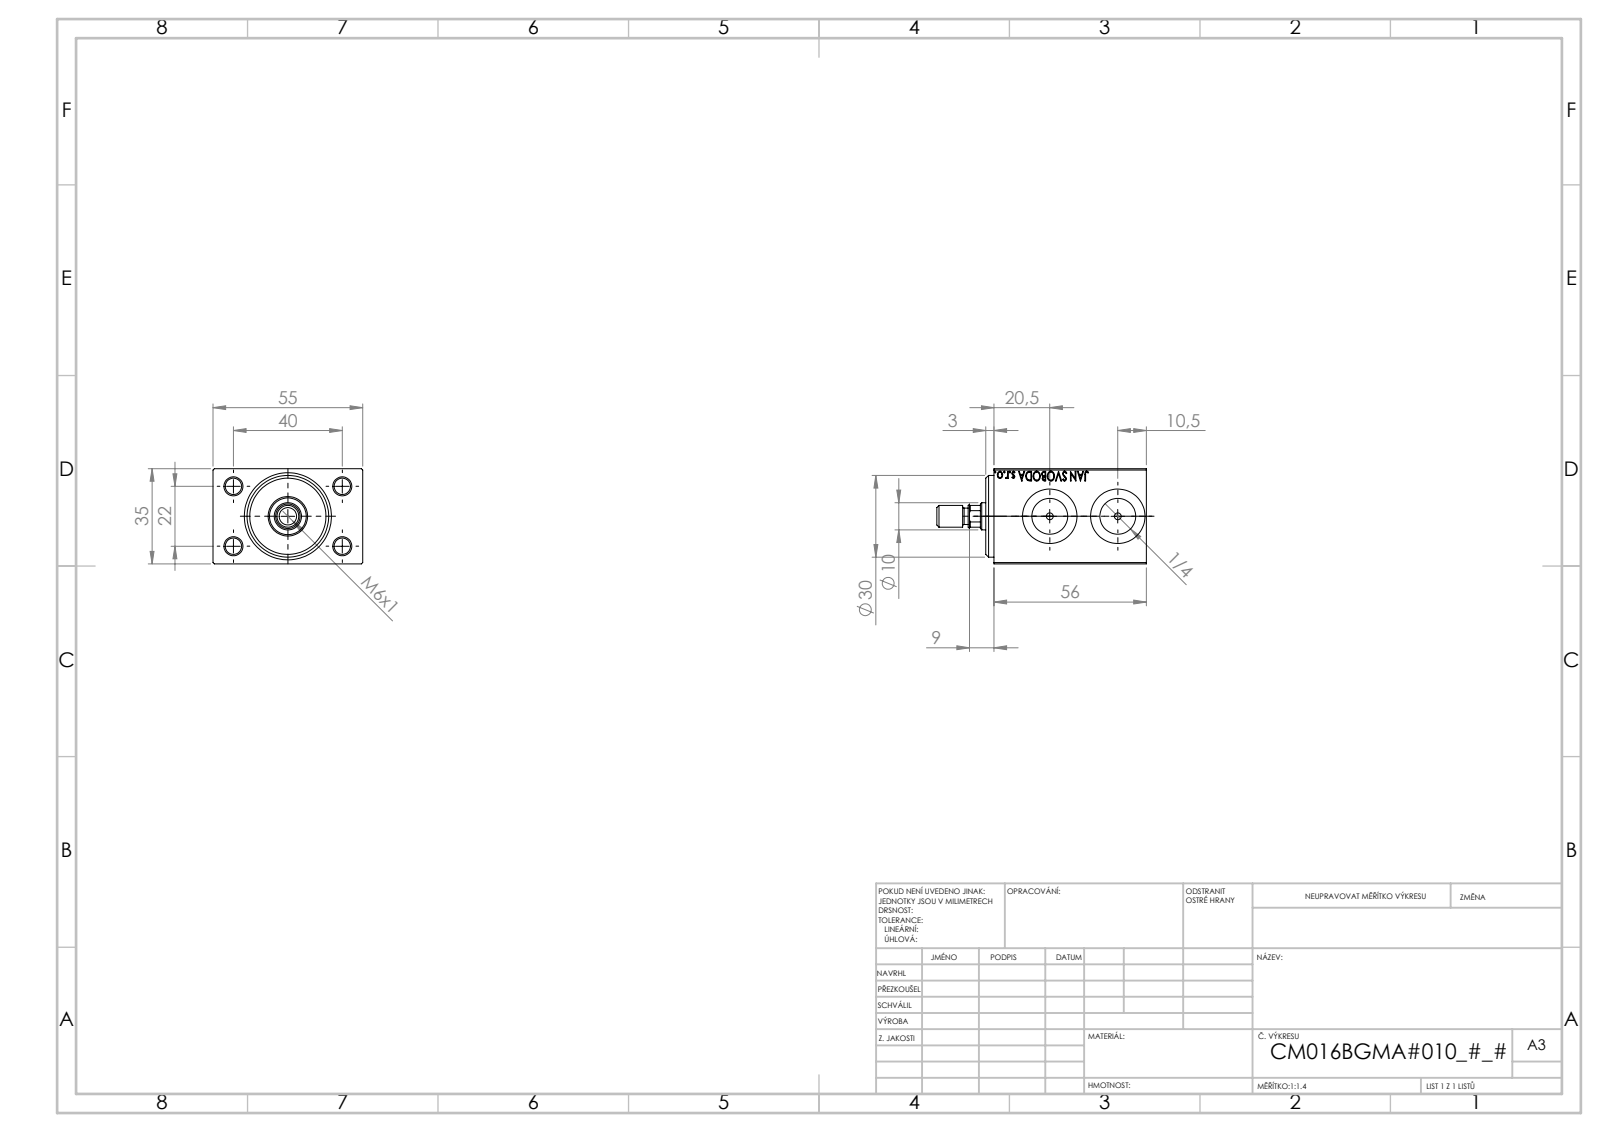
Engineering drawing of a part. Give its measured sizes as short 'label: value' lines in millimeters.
name: V450CM_VC_B; V450CM_B_Body; V450CM_B_VCP; V450CM_MALE_METRIC
written by: SolidWorks 2019 (CONFIG_CONTROL_DESIGN)
unit: mm
bodies: 4 solids, 895 faces (405 planar, 58 cylindrical, 432 other)
size: 77 × 55 × 35
volume: 103 079 mm³; area: 25 484 mm²
holes: 4× ⌀6, 2× ⌀2.5, 2× ⌀13.16, 2× ⌀20, 1× ⌀4.5, 1× ⌀10, 1× ⌀13.5, 1× ⌀14.5, 1× ⌀16, 1× ⌀18, 1× ⌀30
bosses: 1× ⌀8, 1× ⌀6
rounds: 1× R4.5
face distances: 35, 5, 51, 55, 56, 8, 3, 59, 54, 46
hole spacings: 22.83, 22, 40, 45.65, 25
